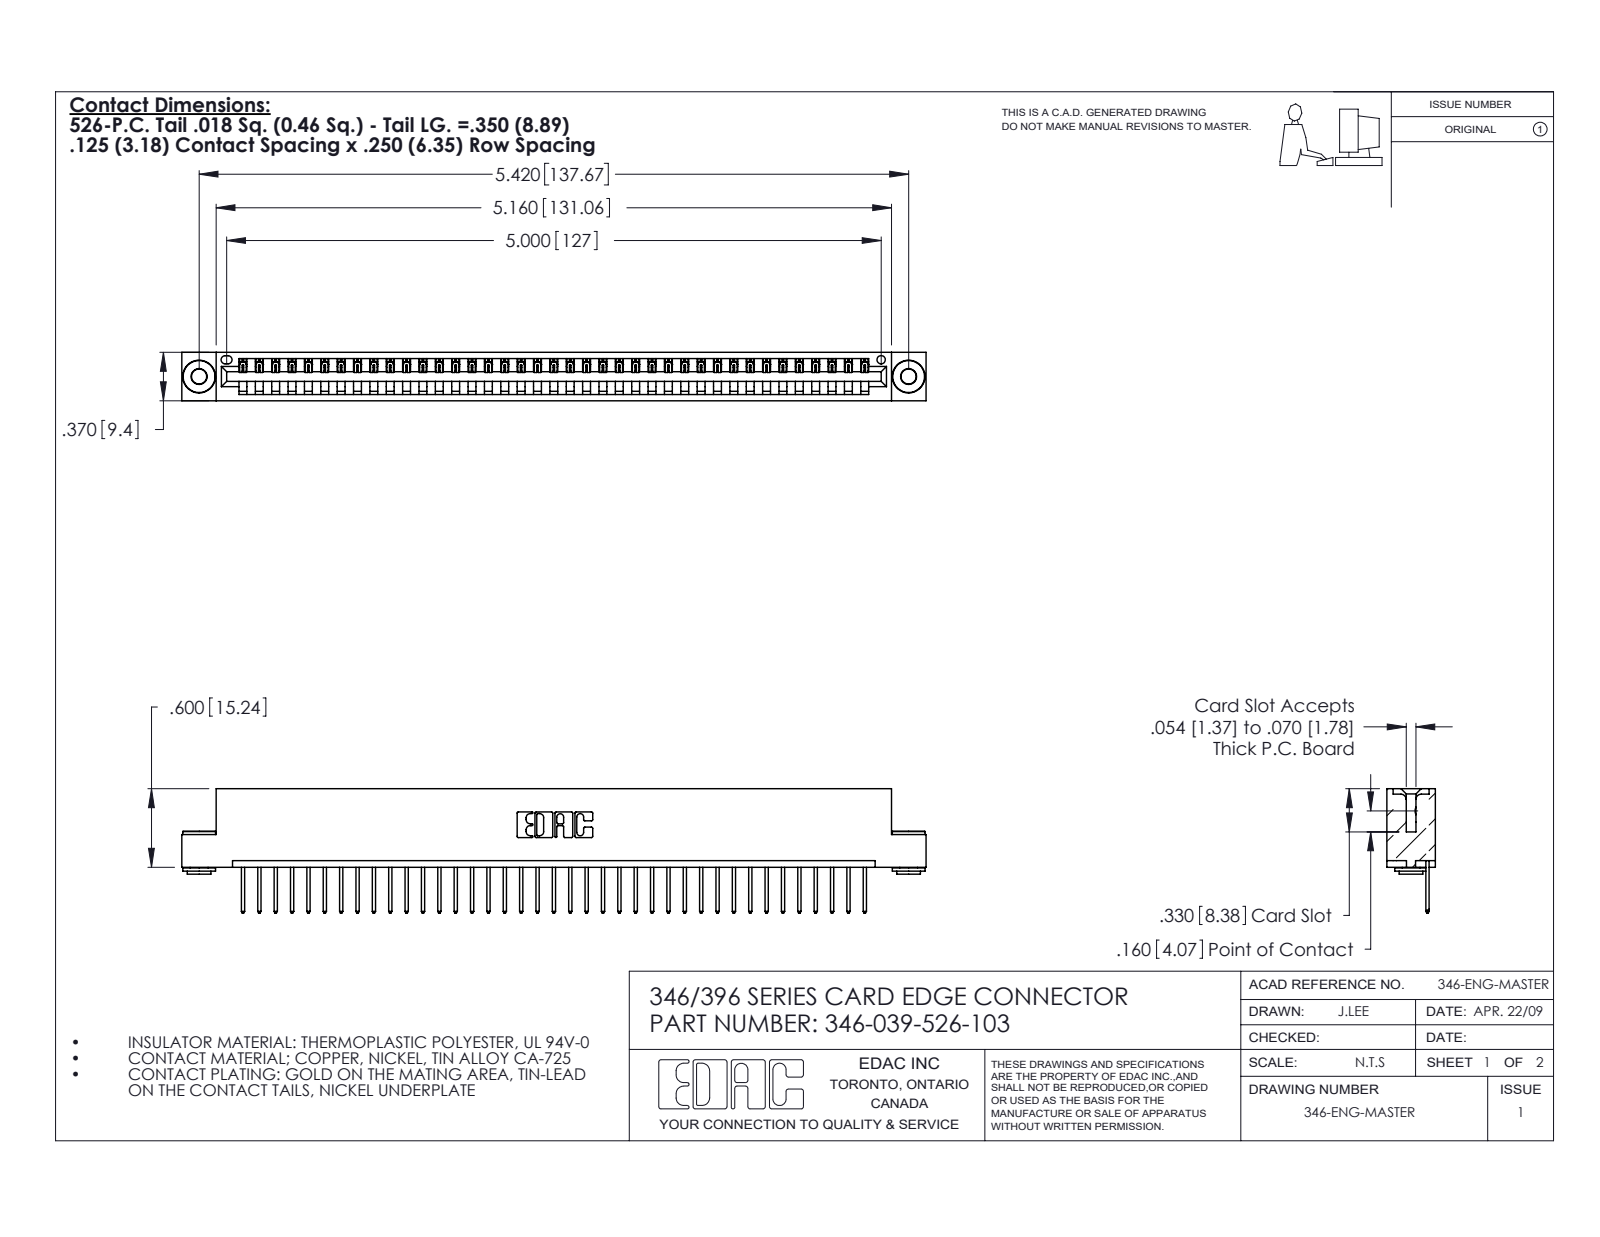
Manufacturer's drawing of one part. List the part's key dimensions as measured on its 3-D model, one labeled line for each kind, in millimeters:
Part name (STEP PRODUCT): 346 Part_Flush Mounting Lugs - 0.156 Dia-TH; 346-039-526-103; 345-292-001_345-293-126; 345-250-002_345-250-002-102
STEP written by: SolidWorks 2020 (CONFIG_CONTROL_DESIGN)
Units: millimetres
Bodies: 42 solids, 2436 faces (1660 planar, 768 cylindrical, 8 other)
Overall size (bounding box): 144.4 × 24.1 × 9.4
Volume: 13 800 mm³ · Surface area: 17 390 mm²
Round holes (diameter × count): ⌀2.9 ×2, ⌀4 ×2, ⌀1.6 ×1
Round bosses / shafts (diameter × count): ⌀6.4 ×2, ⌀4.6 ×2, ⌀3.5 ×2
Partial cylindrical surfaces — rounded edges, fillets, slot ends (radius × count): R0.2 ×78, R0.3 ×78, R0.3 ×22, R0.2 ×6, R0.8 ×6, R0.7 ×3, R0.8 ×2, R1 ×2
Main face-to-face distances: 1.2, 8.2, 9.4, 6.4, 0.6, 1.8, 7.6, 3.8, 5.6, 2.5
Hole centre spacings: 6.2, 132.4, 137.7
